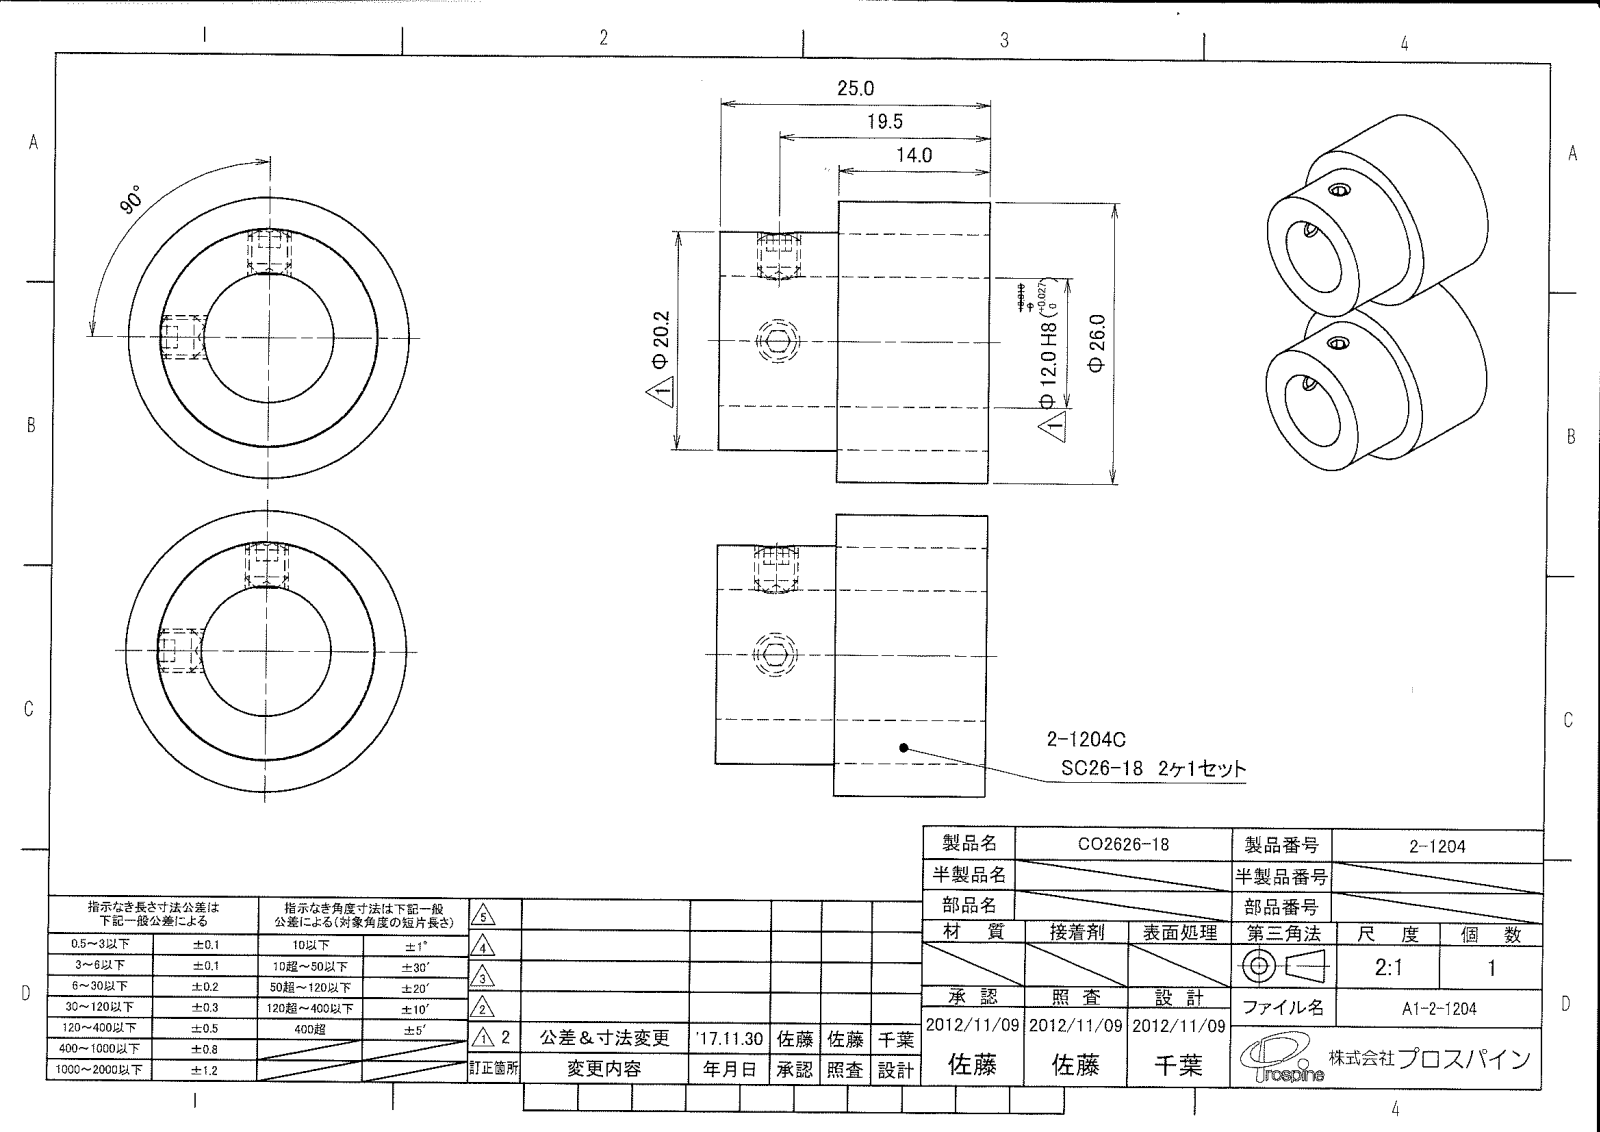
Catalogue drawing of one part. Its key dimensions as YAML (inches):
step_written_by: "PSStep 10.0 (CONFIG_CONTROL_DESIGN)"
units: inches
bodies: {solids: 6, faces: 56, planar: 33, cylindrical: 11, other: 12}
overall_size: [1.024, 1.024, 0.984]
volume: 0.501
surface_area: 8.885
round_holes:
  - {diameter: 0.13, count: 2}
  - {diameter: 0.472, count: 1}
  - {diameter: 0.787, count: 1}
round_bosses_or_shafts:
  - {diameter: 0.157, count: 2}
  - {diameter: 1.024, count: 1}
  - {diameter: 0.795, count: 1}
face_to_face_distances: [0.551, 0.433, 0.984, 0.079, 0.368, 0.294, 0.289, 0.372]
